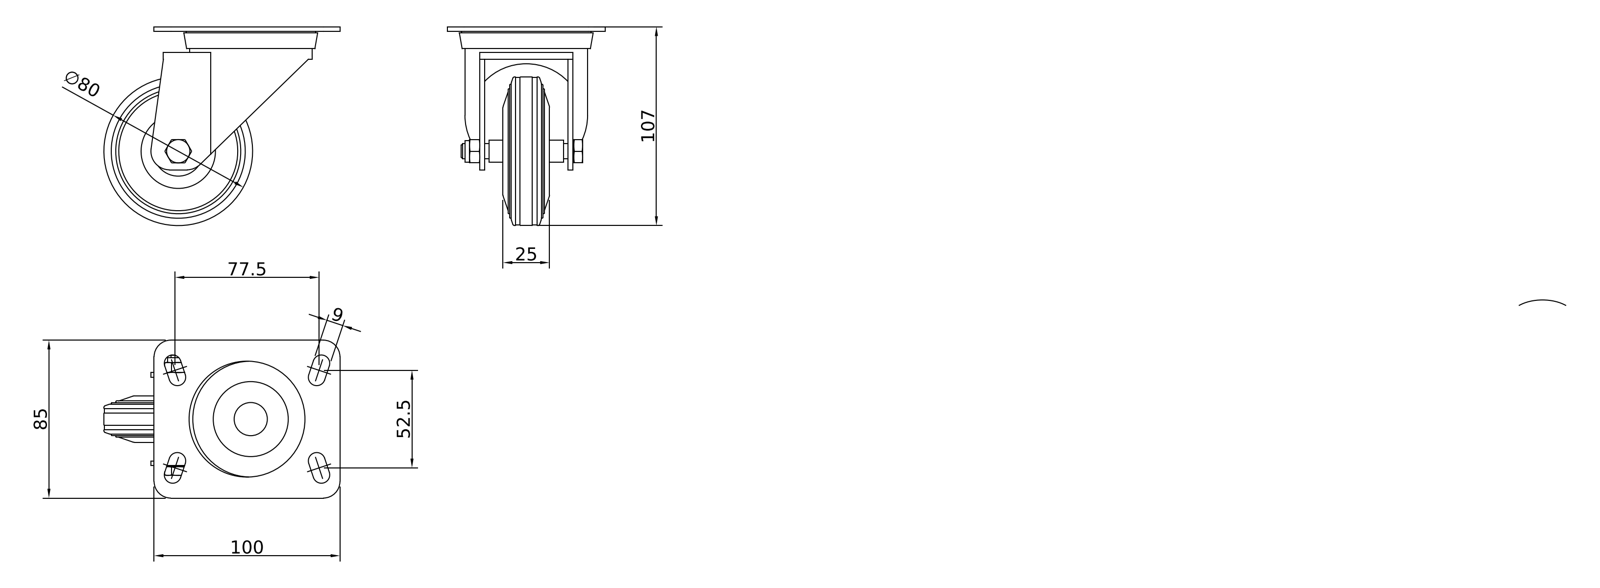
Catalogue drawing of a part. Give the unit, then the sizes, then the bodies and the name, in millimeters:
Units: millimetres
Overall size (bounding box): 127 × 107 × 85
Round holes (diameter × count): ⌀9 ×1, ⌀12 ×1, ⌀40.35 ×1, ⌀61 ×1, ⌀62.35 ×1
Round bosses / shafts (diameter × count): ⌀80 ×1, ⌀79.4 ×1, ⌀69.6 ×1, ⌀66 ×1, ⌀11.63 ×1, ⌀8 ×1
Partial cylindrical surfaces — rounded edges, fillets, slot ends (radius × count): R4.5 ×8, R9 ×4, R10 ×2, R31.18 ×1
Main face-to-face distances: 2.5, 47.5, 11.5, 14, 50, 45, 37.5, 10, 12.5, 35
Hole centre spacings: 2
Volume: 173 978 mm³ · Surface area: 59 090 mm²
Bodies: 3 solids, 169 faces (68 planar, 37 cylindrical, 64 other)
Part name (STEP PRODUCT): CRUST0000195; 440000025826; 440000025825; 440000025824
STEP written by: Autodesk Inventor 2022 (AUTOMOTIVE_DESIGN)
